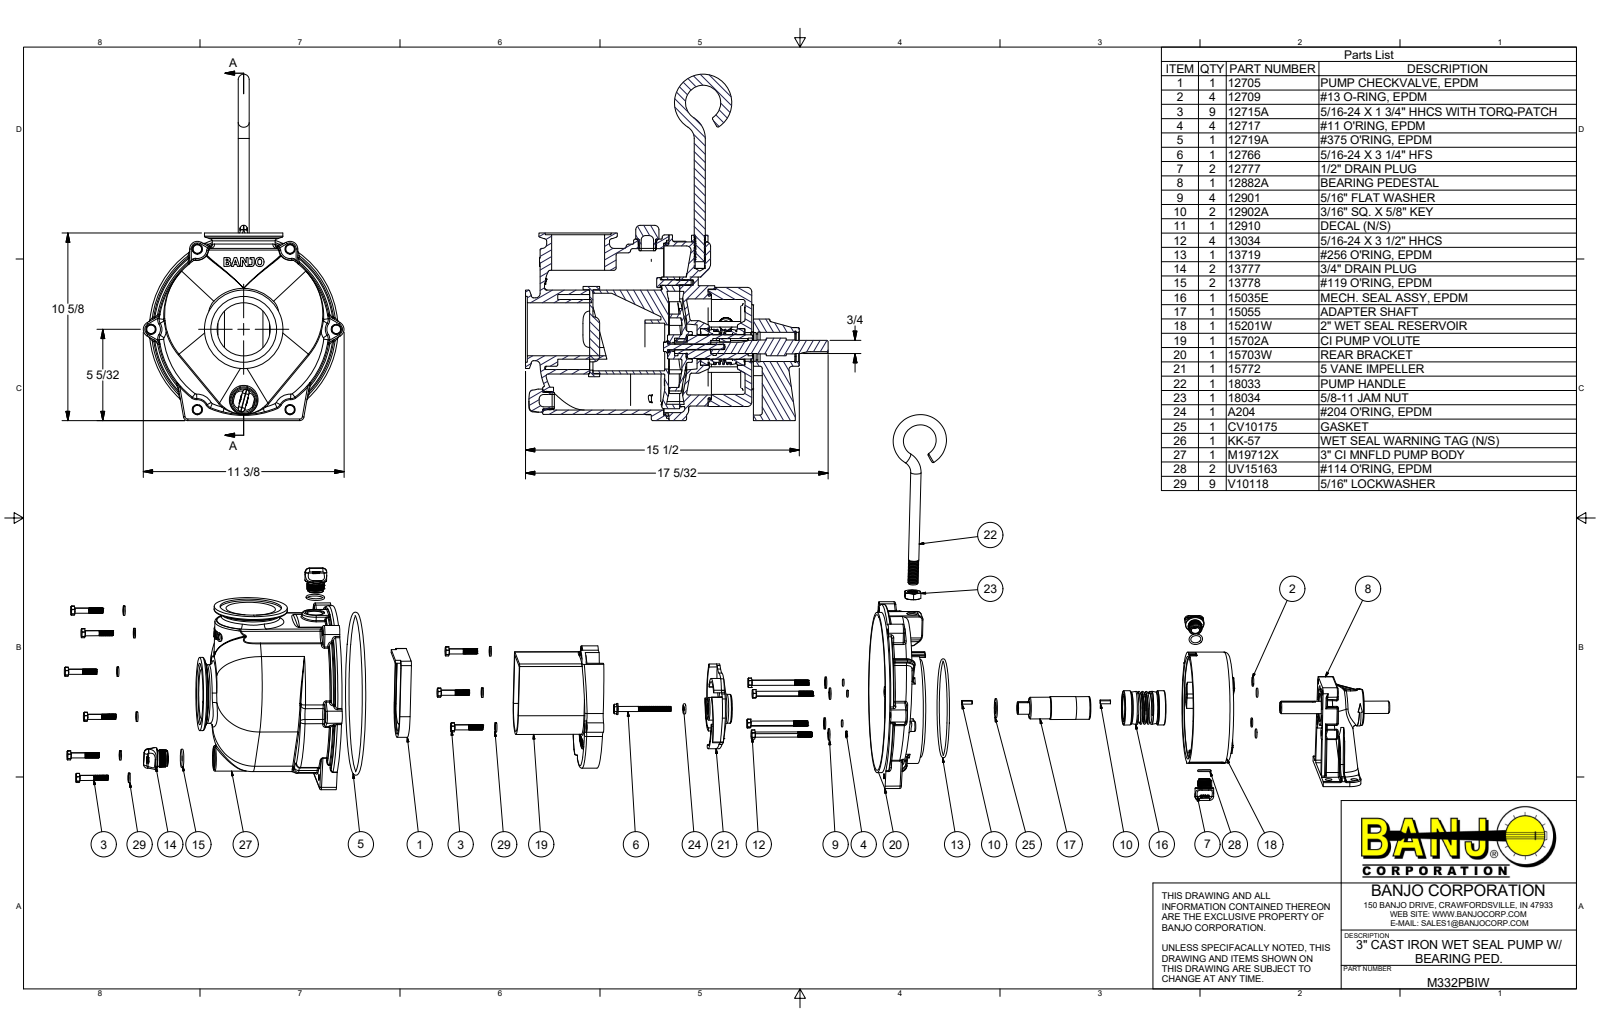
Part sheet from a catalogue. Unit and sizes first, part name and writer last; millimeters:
Units: millimetres
Overall size (bounding box): 498.36 × 435.56 × 288.93
Round holes (diameter × count): ⌀6.78 ×14, ⌀8.18 ×9, ⌀8.2 ×9, ⌀8.73 ×5, ⌀7.95 ×4, ⌀8.13 ×4, ⌀10.32 ×4, ⌀10.79 ×4, ⌀14.25 ×4, ⌀23.81 ×4, ⌀13.92 ×3, ⌀1.98 ×2
Round bosses / shafts (diameter × count): ⌀7.02 ×260, ⌀7.94 ×14, ⌀14.81 ×9, ⌀17.48 ×4, ⌀9.68 ×4, ⌀112.78 ×2, ⌀90.49 ×2, ⌀44.45 ×2
Partial cylindrical surfaces — rounded edges, fillets, slot ends (radius × count): R1.52 ×143, R3.17 ×117, R2.29 ×81, R0.76 ×32, R3.51 ×26, R2.38 ×22, R12.7 ×18, R9.53 ×17
Main face-to-face distances: 6.35, 119.22, 4.76, 4.57, 9.53, 56.51, 62.71, 0.38, 56.89, 119.6
Hole centre spacings: 133.35, 46.03, 65.09, 65.11, 46.04, 230.97, 20.03, 41.94
Volume: 4 390 000 mm³ · Surface area: 1 310 000 mm²
Bodies: 64 solids, 6849 faces (1485 planar, 2193 cylindrical, 3171 other)
Part name (STEP PRODUCT): M332PBIW; 15703W; 15201W; M19712X (+8 more)
STEP written by: Autodesk Inventor 2017 (AUTOMOTIVE_DESIGN)
